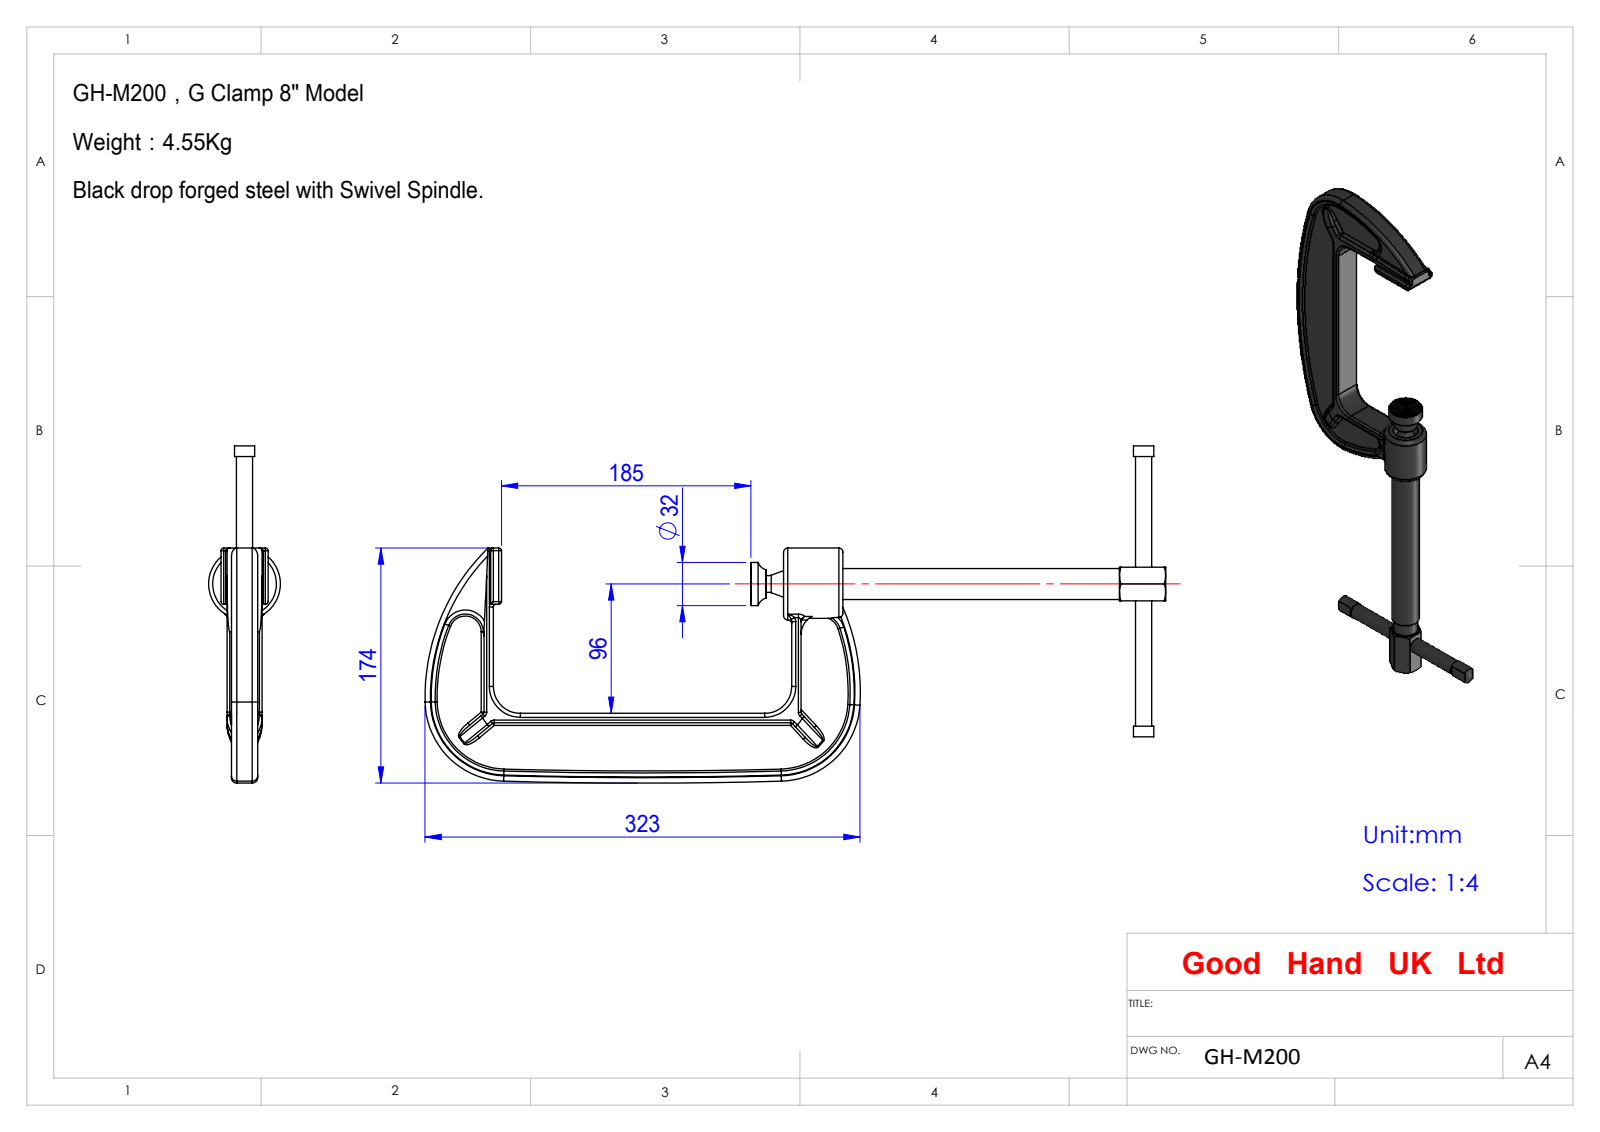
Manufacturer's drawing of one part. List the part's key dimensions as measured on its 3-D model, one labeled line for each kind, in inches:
Part name (STEP PRODUCT): GH-M200
STEP written by: SolidWorks 2008 (CONFIG_CONTROL_DESIGN)
Units: inches
Bodies: 4 solids, 337 faces (58 planar, 104 cylindrical, 175 other)
Overall size (bounding box): 20.793 × 9.931 × 1.437
Volume: 35.07 in³ · Surface area: 170.9 in²
Round holes (diameter × count): ⌀0.472 ×1, ⌀0.551 ×1, ⌀0.591 ×1, ⌀0.843 ×1
Round bosses / shafts (diameter × count): ⌀1.437 ×1, ⌀1.102 ×1, ⌀0.906 ×1, ⌀0.591 ×1
Partial cylindrical surfaces — rounded edges, fillets, slot ends (radius × count): R0.079 ×51, R0.118 ×10, R0.039 ×6, R0.787 ×2, R2.362 ×2, R6.102 ×1, R6.299 ×1
Main face-to-face distances: 0.61, 0.207, 0.817, 0.128, 0.896, 0.079, 0.689, 0.236, 8.465, 0.984
